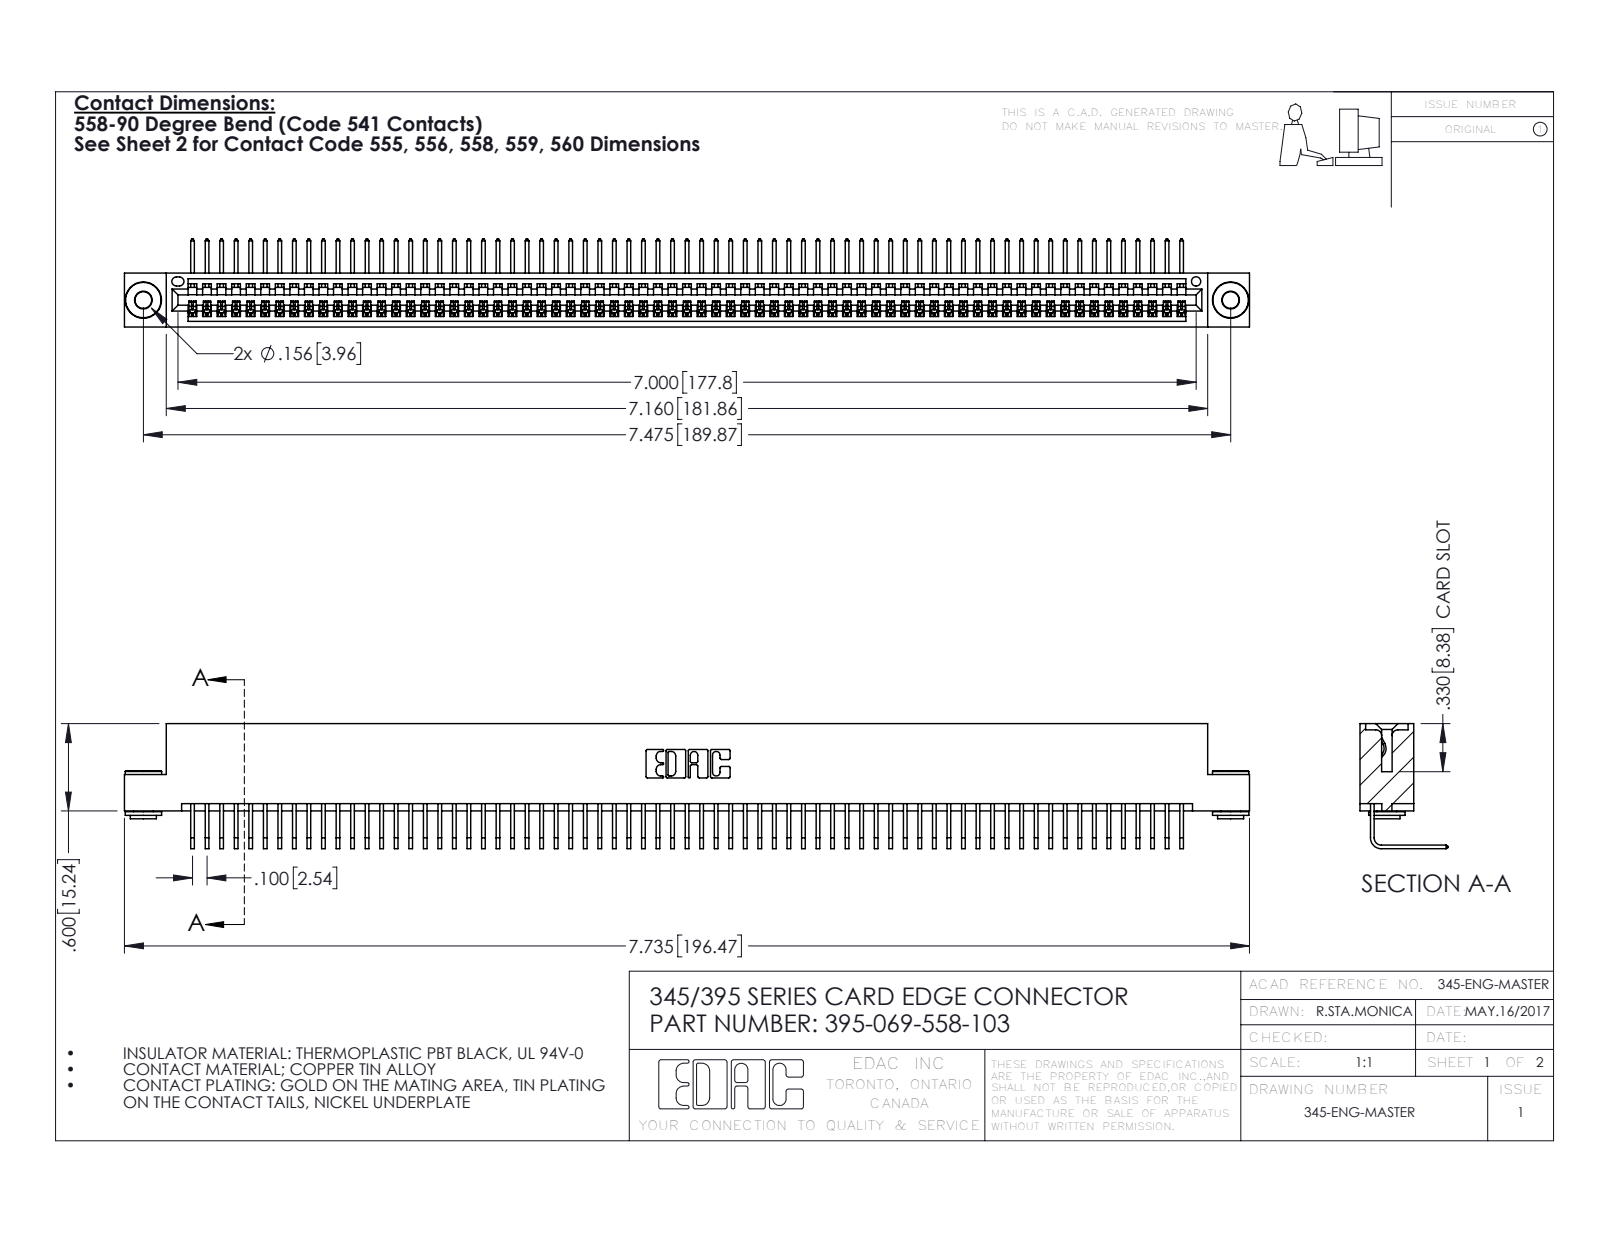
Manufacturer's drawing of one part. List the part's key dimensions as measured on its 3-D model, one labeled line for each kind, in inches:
Part name (STEP PRODUCT): 345-292-001_558 Tail - 2; 345 Part_Flush Mounting Lugs - 0.156 Dia-TH; 345-250-002_345-250-002-102; 395-069-558-103
STEP written by: SolidWorks 2016 (CONFIG_CONTROL_DESIGN)
Units: inches
Bodies: 72 solids, 4304 faces (2988 planar, 1308 cylindrical, 8 other)
Overall size (bounding box): 7.735 × 0.859 × 0.605
Volume: 1.167 in³ · Surface area: 42.4 in²
Round holes (diameter × count): ⌀0.116 ×2, ⌀0.156 ×2, ⌀0.064 ×1
Round bosses / shafts (diameter × count): ⌀0.25 ×2, ⌀0.18 ×2, ⌀0.136 ×2
Partial cylindrical surfaces — rounded edges, fillets, slot ends (radius × count): R0.006 ×138, R0.01 ×22, R0.007 ×6, R0.031 ×6, R0.026 ×3, R0.031 ×2, R0.04 ×2, R0.014 ×1
Main face-to-face distances: 0.072, 0.298, 0.37, 0.2, 0.025, 0.098, 0.272, 0.225, 0.149, 0.072
Hole centre spacings: 0.27, 7.239, 7.475
